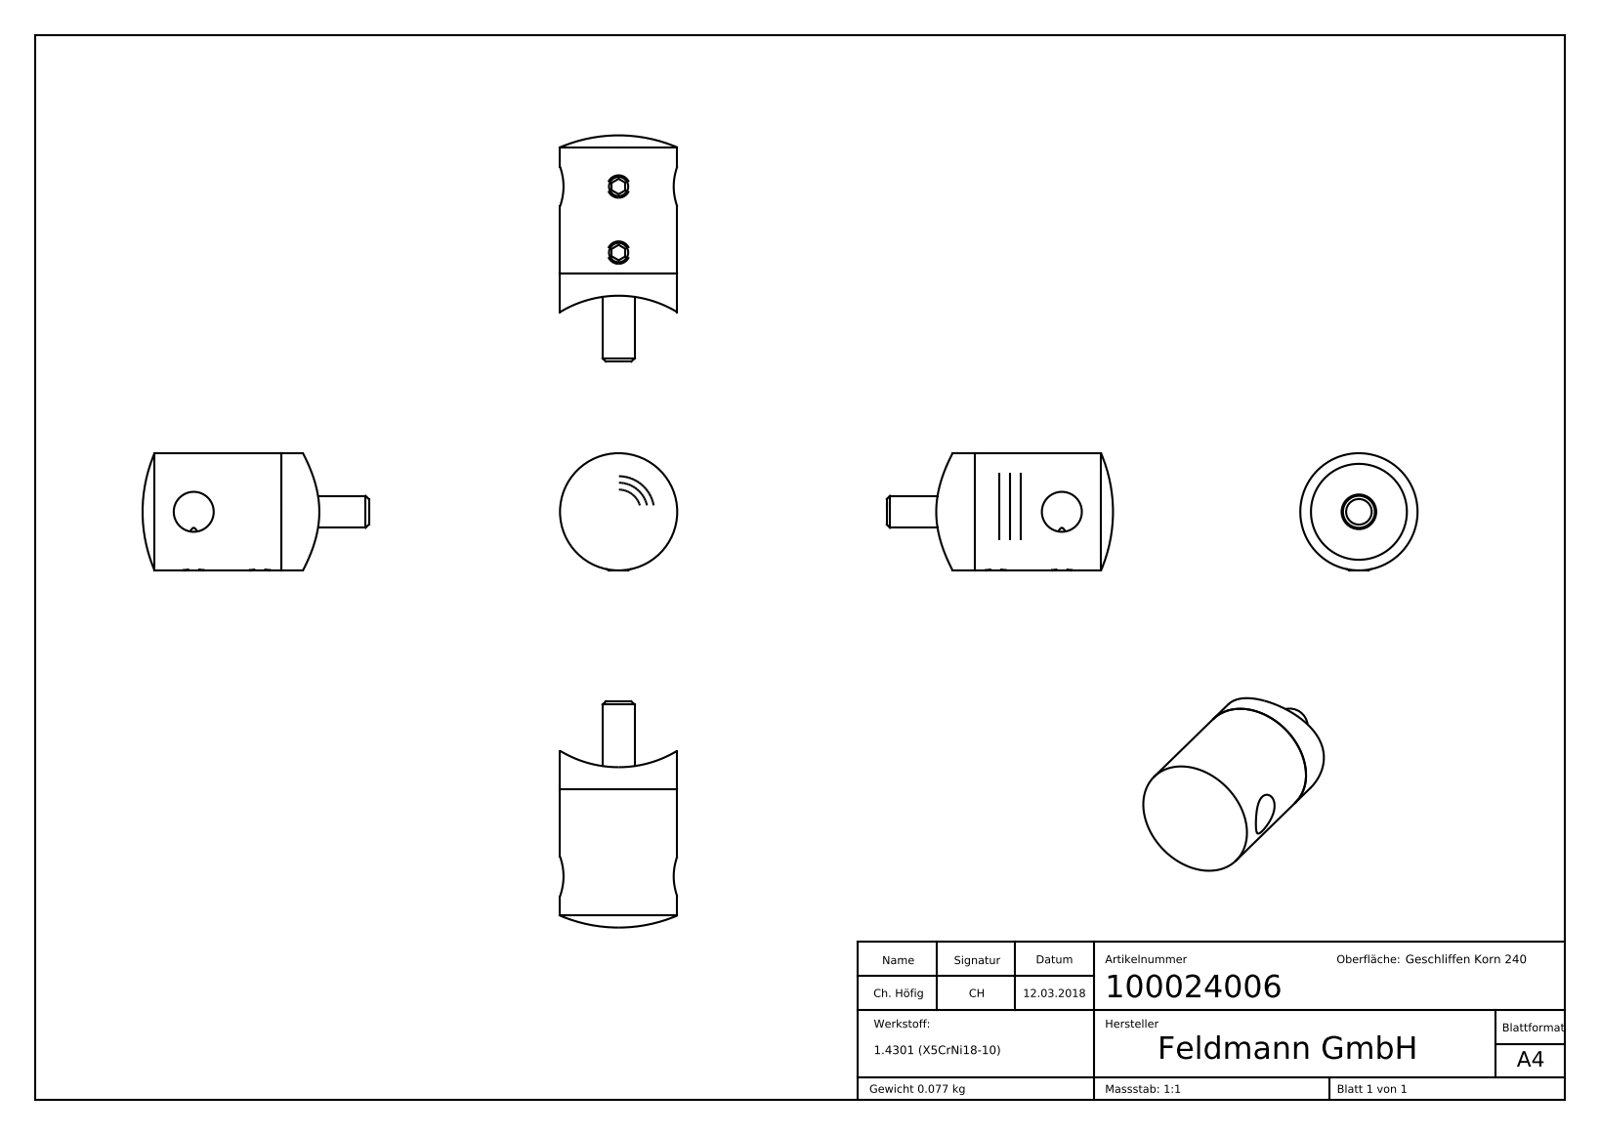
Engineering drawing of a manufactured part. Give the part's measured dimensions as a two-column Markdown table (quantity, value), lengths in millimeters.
| quantity | value |
| --- | --- |
| part name | 100024006; DIN914_DIN 914 M5x5; 10002X00X Teil2; 10002X00X Teil1 (+6 more) |
| STEP written by | SolidWorks 2018 (CONFIG_CONTROL_DESIGN) |
| units | millimeters |
| bodies | 5 solids, 280 faces (143 planar, 15 cylindrical, 122 other) |
| overall size | 42.45 × 24 × 22 |
| volume | 9 691 mm³ |
| surface area | 5 948 mm² |
| round holes (diameter × count) | 4.2 × 2, 6.5 × 1, 7.5 × 1, 12.1 × 1, 18 × 1 |
| round bosses / shafts (diameter × count) | 5 × 2, 22 × 1, 12 × 1, 6 × 1 |
| partial cylindrical surfaces (radius × count) | 21.2 × 1 |
| main face-to-face distances | 2, 10.55, 8.55, 4, 14.45, 16.45, 25, 2.5, 10.73, 23.95 |
| hole center spacings | 12.4 |
